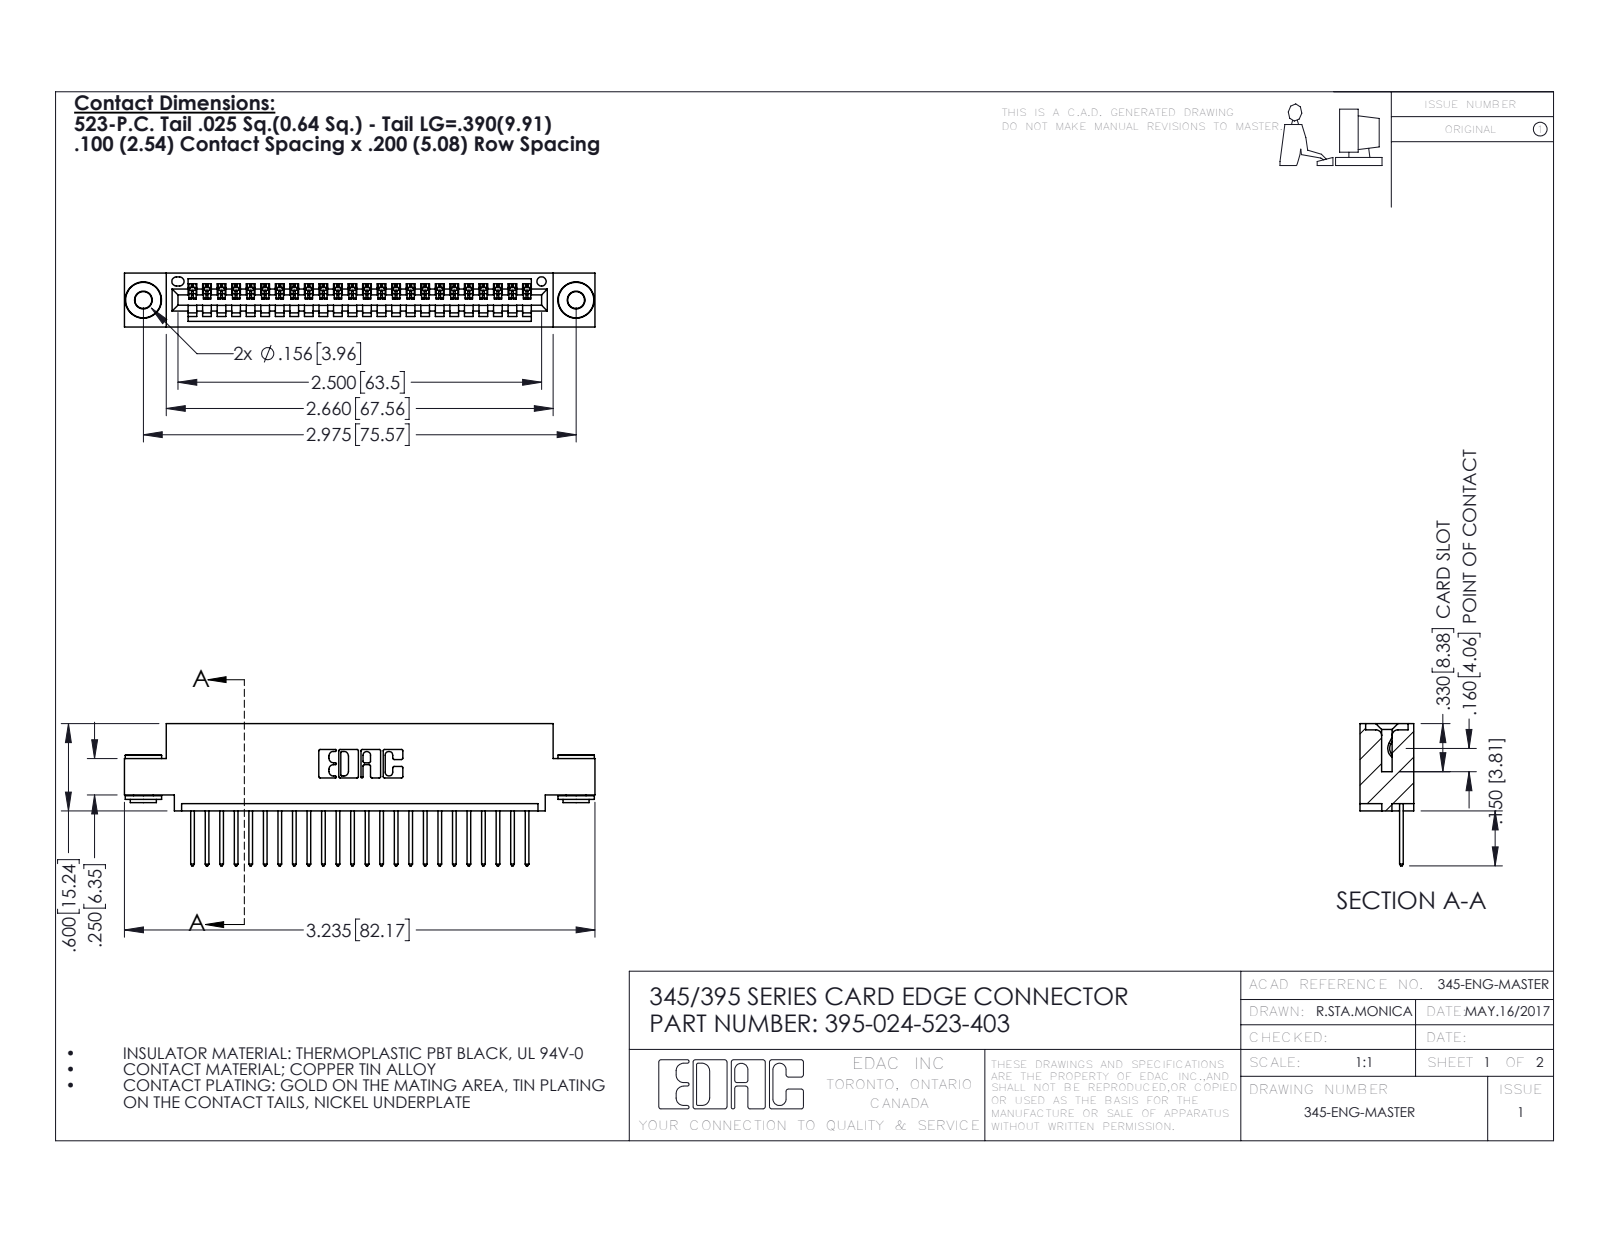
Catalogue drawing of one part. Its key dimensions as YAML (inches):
part_name: "345-250-002_345-250-002-102; 345 Part_0.110 Offset - 0.156 Dia-TH; 345-292-001_345-293-123; 395-024-523-403"
step_written_by: "SolidWorks 2016 (CONFIG_CONTROL_DESIGN)"
units: inches
bodies: {solids: 27, faces: 1560, planar: 1054, cylindrical: 498, other: 8}
overall_size: [3.235, 0.977, 0.37]
volume: 0.463
surface_area: 15.76
round_holes:
  - {diameter: 0.116, count: 2}
  - {diameter: 0.156, count: 2}
  - {diameter: 0.064, count: 1}
round_bosses_or_shafts:
  - {diameter: 0.25, count: 2}
  - {diameter: 0.18, count: 2}
  - {diameter: 0.136, count: 2}
partial_cylinders:
  - {radius: 0.006, count: 48}
  - {radius: 0.01, count: 48}
  - {radius: 0.01, count: 22}
  - {radius: 0.007, count: 6}
  - {radius: 0.031, count: 6}
  - {radius: 0.026, count: 3}
  - {radius: 0.031, count: 2}
  - {radius: 0.04, count: 2}
face_to_face_distances: [0.072, 0.298, 0.37, 0.2, 0.025, 0.098, 0.272, 0.225, 0.149, 0.072]
hole_center_spacings: [0.27, 2.741, 2.975]
